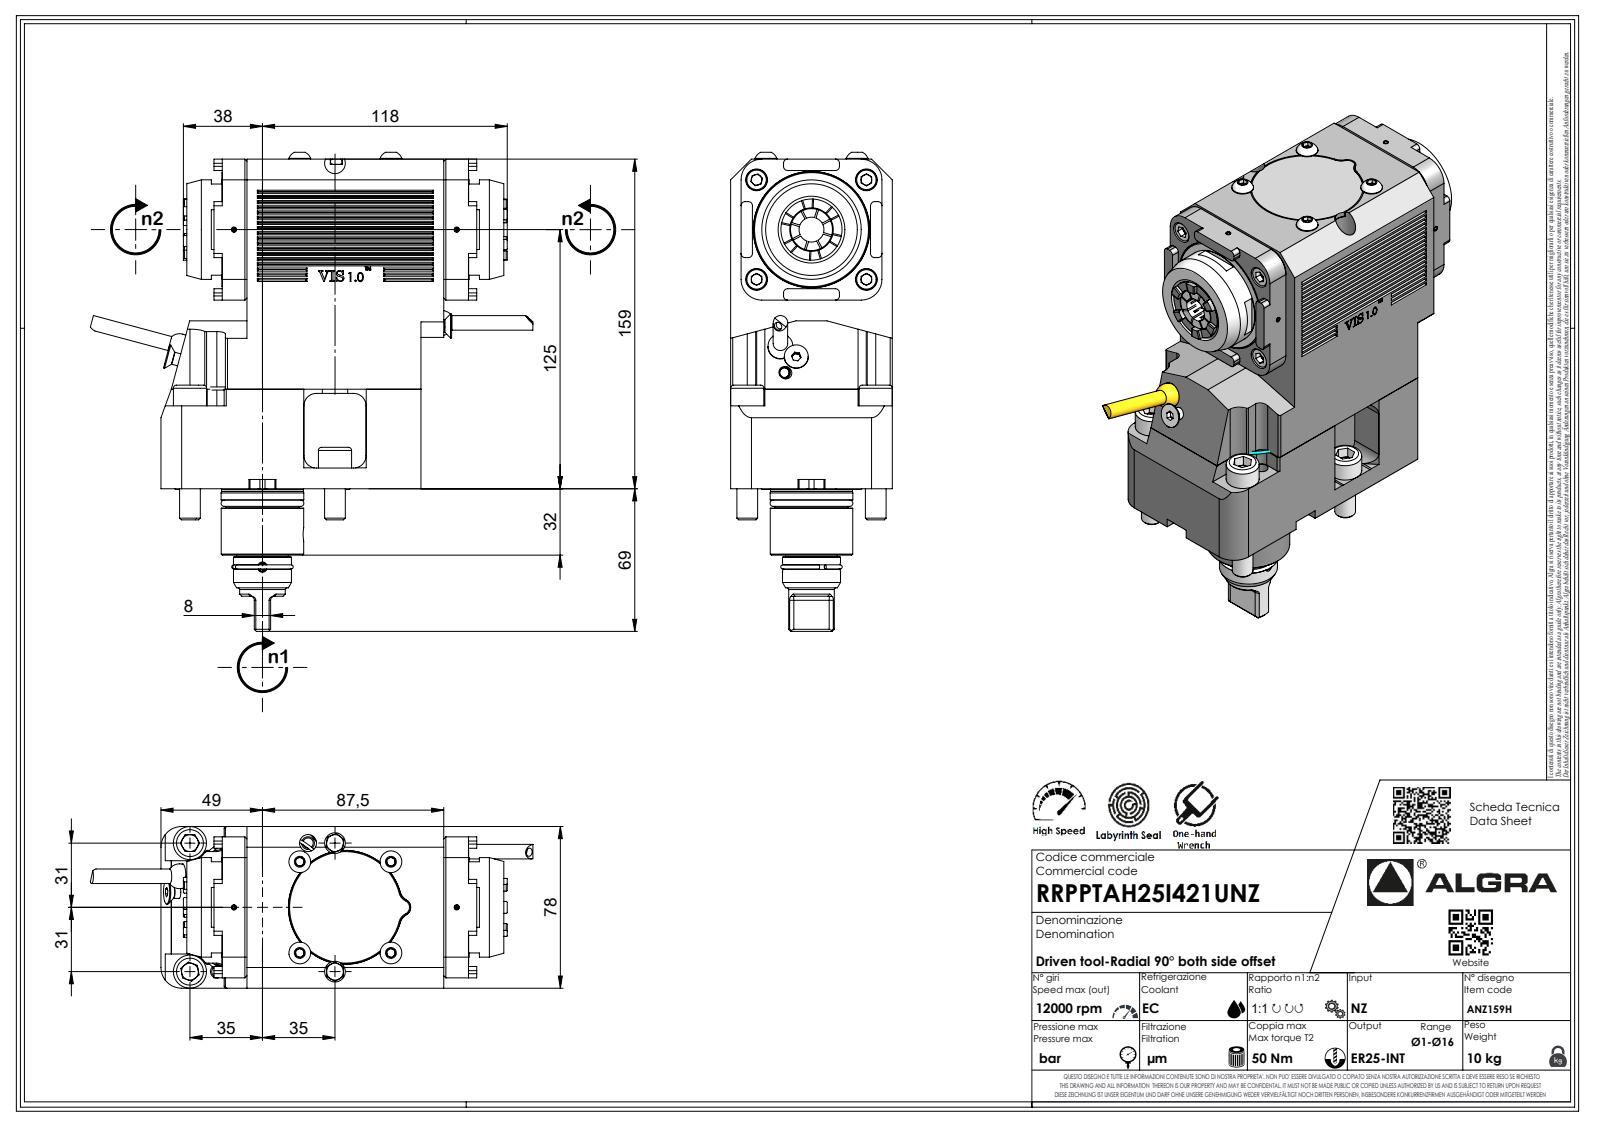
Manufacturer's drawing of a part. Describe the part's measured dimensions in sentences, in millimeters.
The part is named "RRPPTAH25I421UNZ". Its 3-D file was written by "SolidWorks 2023 (AUTOMOTIVE_DESIGN)". It is 1 solid with 590 faces: 382 planar, 115 cylindrical and 93 other. Overall it measures 231.1 by 213.57 by 78 millimeters. Its volume is 1 545 000 cubic millimeters and its surface area 102 989 square millimeters. Round holes: 2 of diameter 4, 1 of diameter 2.1. Round bosses or shafts: 4 of diameter 10.5, 4 of diameter 10, 2 of diameter 16, 2 of diameter 7, 1 of diameter 48, 1 of diameter 39.9, 1 of diameter 39.8, 1 of diameter 39.5. Partial cylindrical surfaces (rounded edges, fillets, slot ends): 23 of radius 2, 8 of radius 1, 7 of radius 0.33, 7 of radius 0.52, 7 of radius 3.7, 6 of radius 10, 2 of radius 3.5, 2 of radius 4.1. The main face-to-face distances are 78, 159, 73, 29, 11.9, 106.9, 17.1, 124, 135.9, 5.
